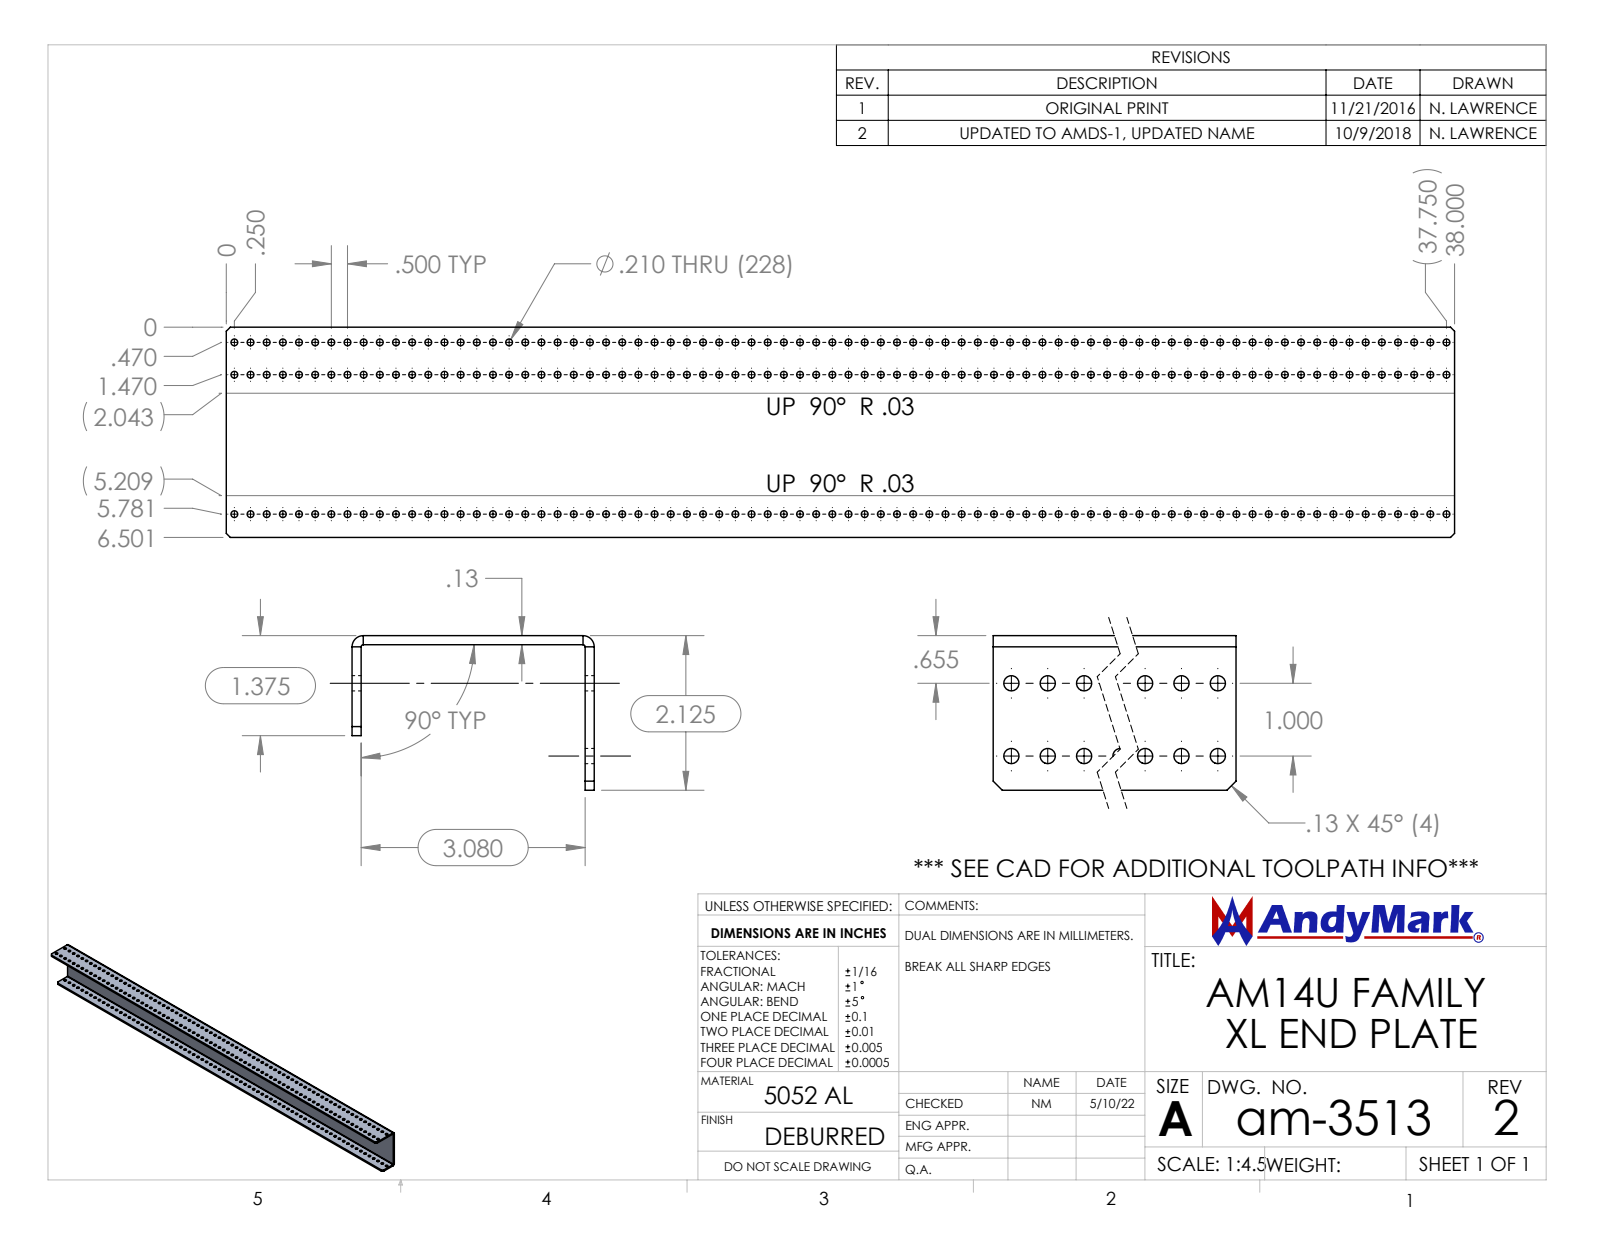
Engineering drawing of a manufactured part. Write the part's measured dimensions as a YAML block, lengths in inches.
part_name: "am-3513 AM14U Family XL End Plate"
step_written_by: "SolidWorks 2021 (CONFIG_CONTROL_DESIGN)"
units: inches
bodies: {solids: 1, faces: 482, planar: 22, cylindrical: 460, other: 0}
overall_size: [38, 3.33, 2.125]
volume: 29.89
surface_area: 508.1
round_holes:
  - {diameter: 0.21, count: 152}
partial_cylinders:
  - {radius: 0.029, count: 2}
  - {radius: 0.154, count: 2}
face_to_face_distances: [0.125, 3.205, 3.33, 3.08, 1.375, 1.25, 2.125, 2, 0.75, 38]
hole_center_spacings: [0.5, 1, 1.5, 2, 2.5, 3, 3.5, 4]
